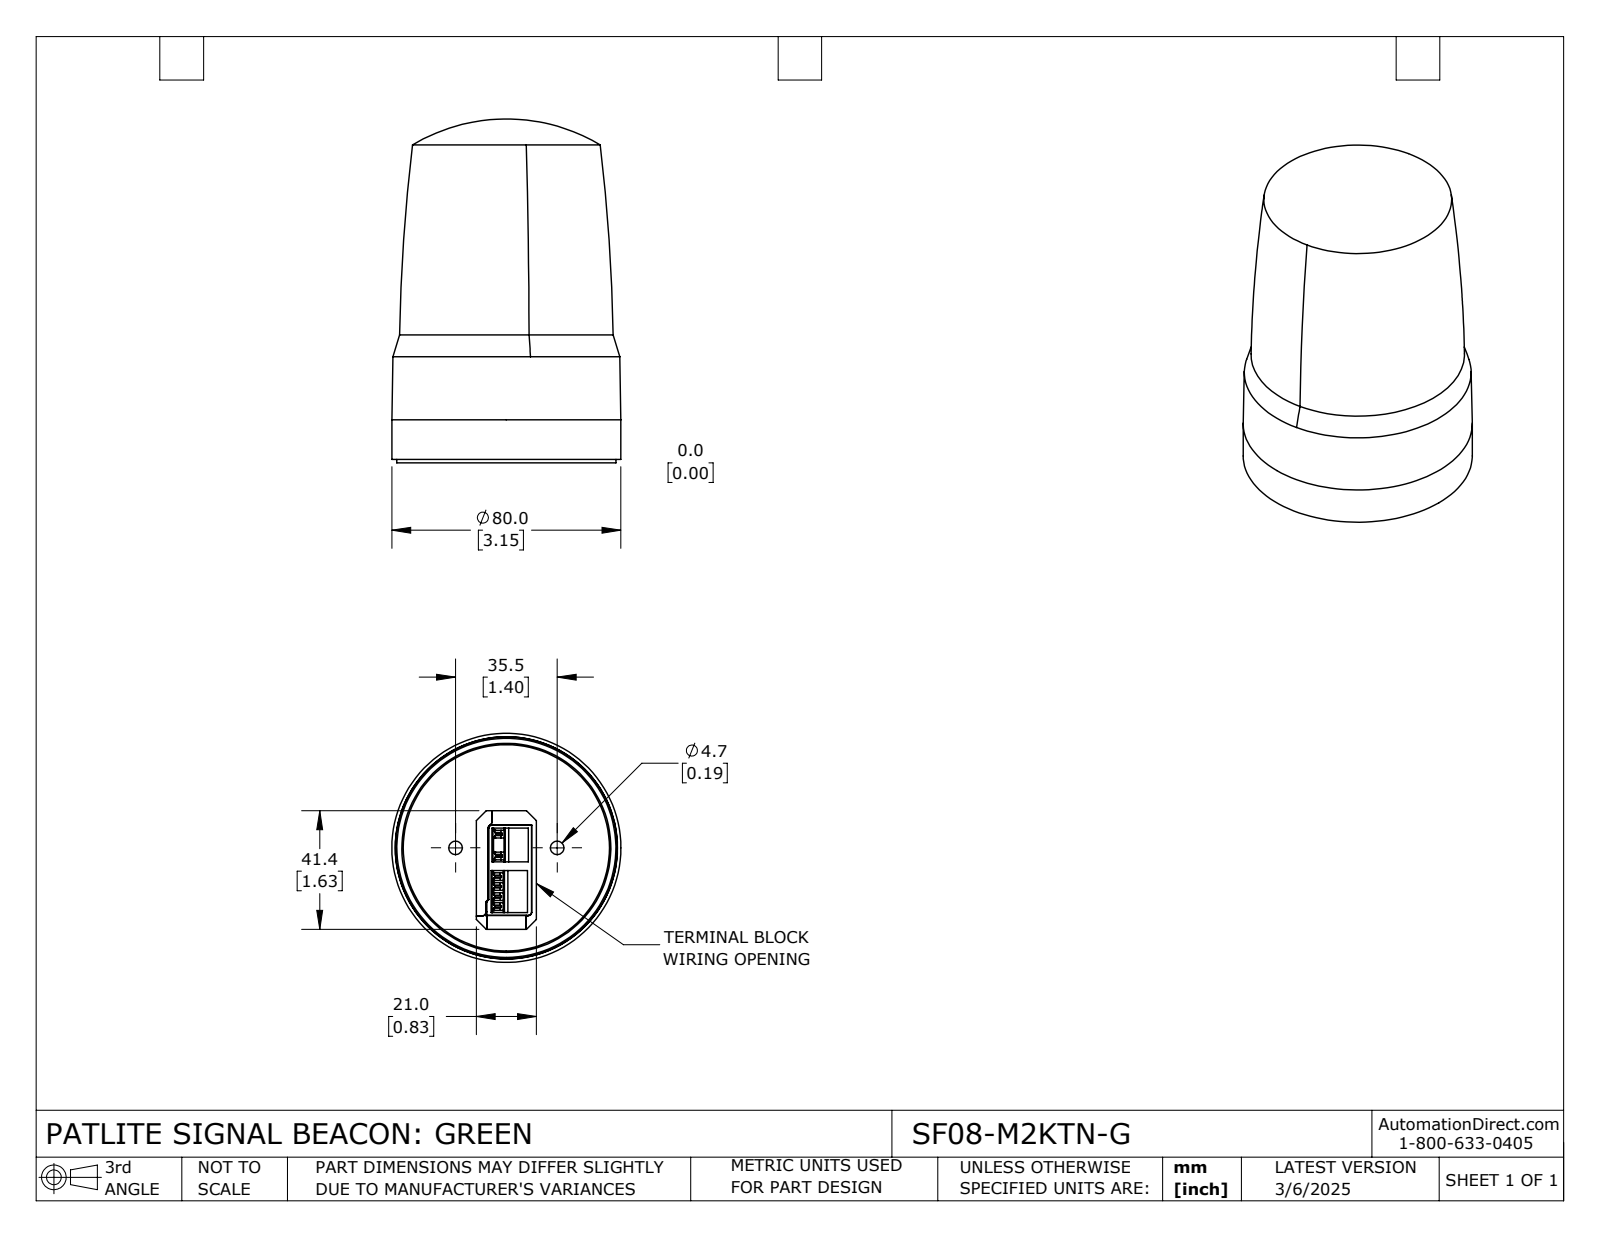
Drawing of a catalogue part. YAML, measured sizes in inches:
part_name: "SF08-M2KTN-G"
step_written_by: "SolidWorks 2024 (CONFIG_CONTROL_DESIGN)"
units: inches
bodies: {solids: 2, faces: 287, planar: 199, cylindrical: 23, other: 65}
overall_size: [4.724, 3.15, 3.15]
volume: 29.01
surface_area: 81.21
round_holes:
  - {diameter: 0.185, count: 2}
  - {diameter: 0.48, count: 2}
  - {diameter: 2.874, count: 1}
round_bosses_or_shafts:
  - {diameter: 3.15, count: 1}
  - {diameter: 3.012, count: 1}
  - {diameter: 2.937, count: 1}
  - {diameter: 2.835, count: 1}
partial_cylinders:
  - {radius: 1.319, count: 1}
  - {radius: 1.362, count: 1}
face_to_face_distances: [0.248, 0.185, 0.433, 0.071, 0.504, 0.256, 0.059, 0.374, 0.126, 0.13]
hole_center_spacings: [0.699, 1.398]
